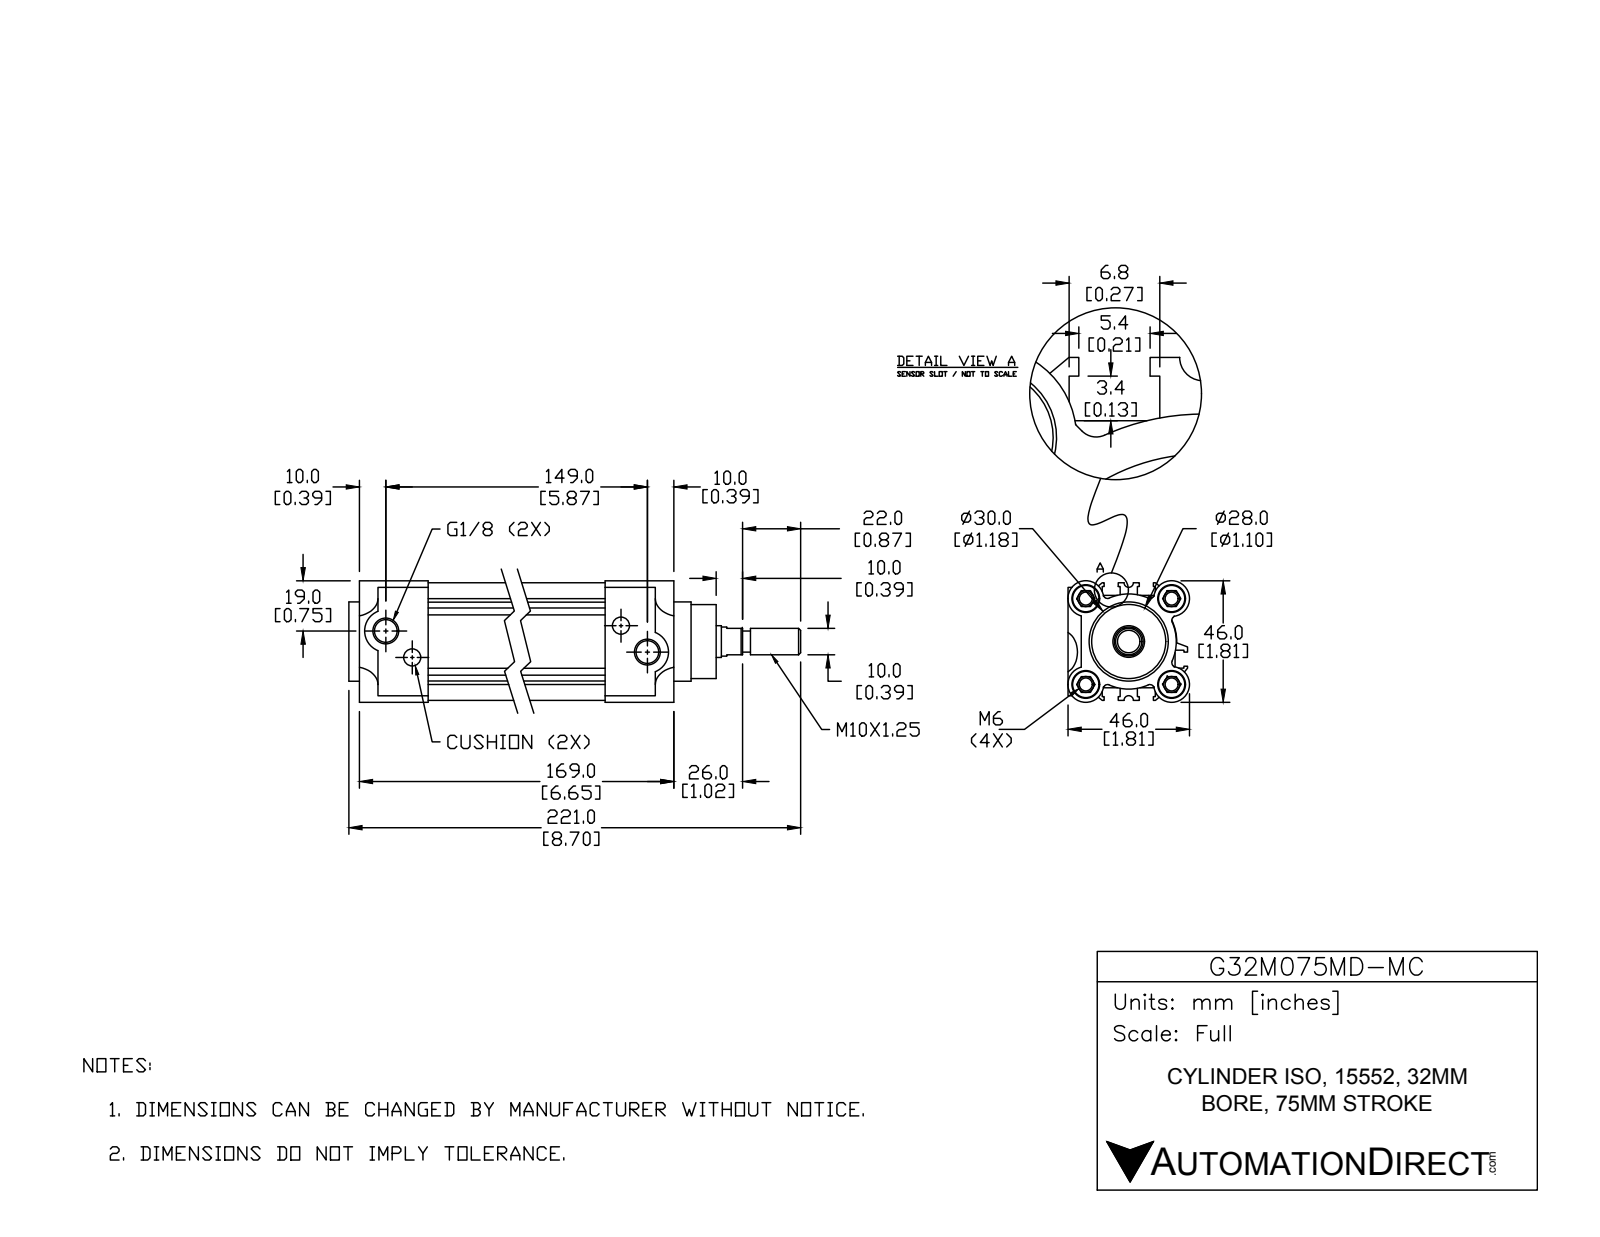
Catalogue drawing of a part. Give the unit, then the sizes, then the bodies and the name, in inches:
Units: inches
Overall size (bounding box): 8.701 × 1.811 × 1.811
Round holes (diameter × count): ⌀0.194 ×4, ⌀0.413 ×4, ⌀0.256 ×2, ⌀0.337 ×2, ⌀0.472 ×1
Round bosses / shafts (diameter × count): ⌀0.394 ×5, ⌀1.26 ×1, ⌀1.181 ×1, ⌀1.102 ×1, ⌀0.433 ×1, ⌀0.315 ×1
Partial cylindrical surfaces — rounded edges, fillets, slot ends (radius × count): R0.004 ×12, R0.059 ×6, R0.236 ×4, R0.266 ×4, R0.069 ×2, R0.315 ×2, R0.709 ×1, R0.717 ×1
Main face-to-face distances: 1.565, 0.187, 0.276, 4.331, 1.378, 1.004, 0.268, 0.748, 0.48, 1.272
Hole centre spacings: 0.905, 1.28, 0.557, 1.809, 5.473, 5.101, 5.874
Volume: 14.82 in³ · Surface area: 136 in²
Bodies: 4 solids, 411 faces (229 planar, 138 cylindrical, 44 other)
Part name (STEP PRODUCT): 32-HL; G32M075MD-MC; 32-75-73.5-B; 32121-HR (+1 more)
STEP written by: SolidWorks 2015 (CONFIG_CONTROL_DESIGN)
